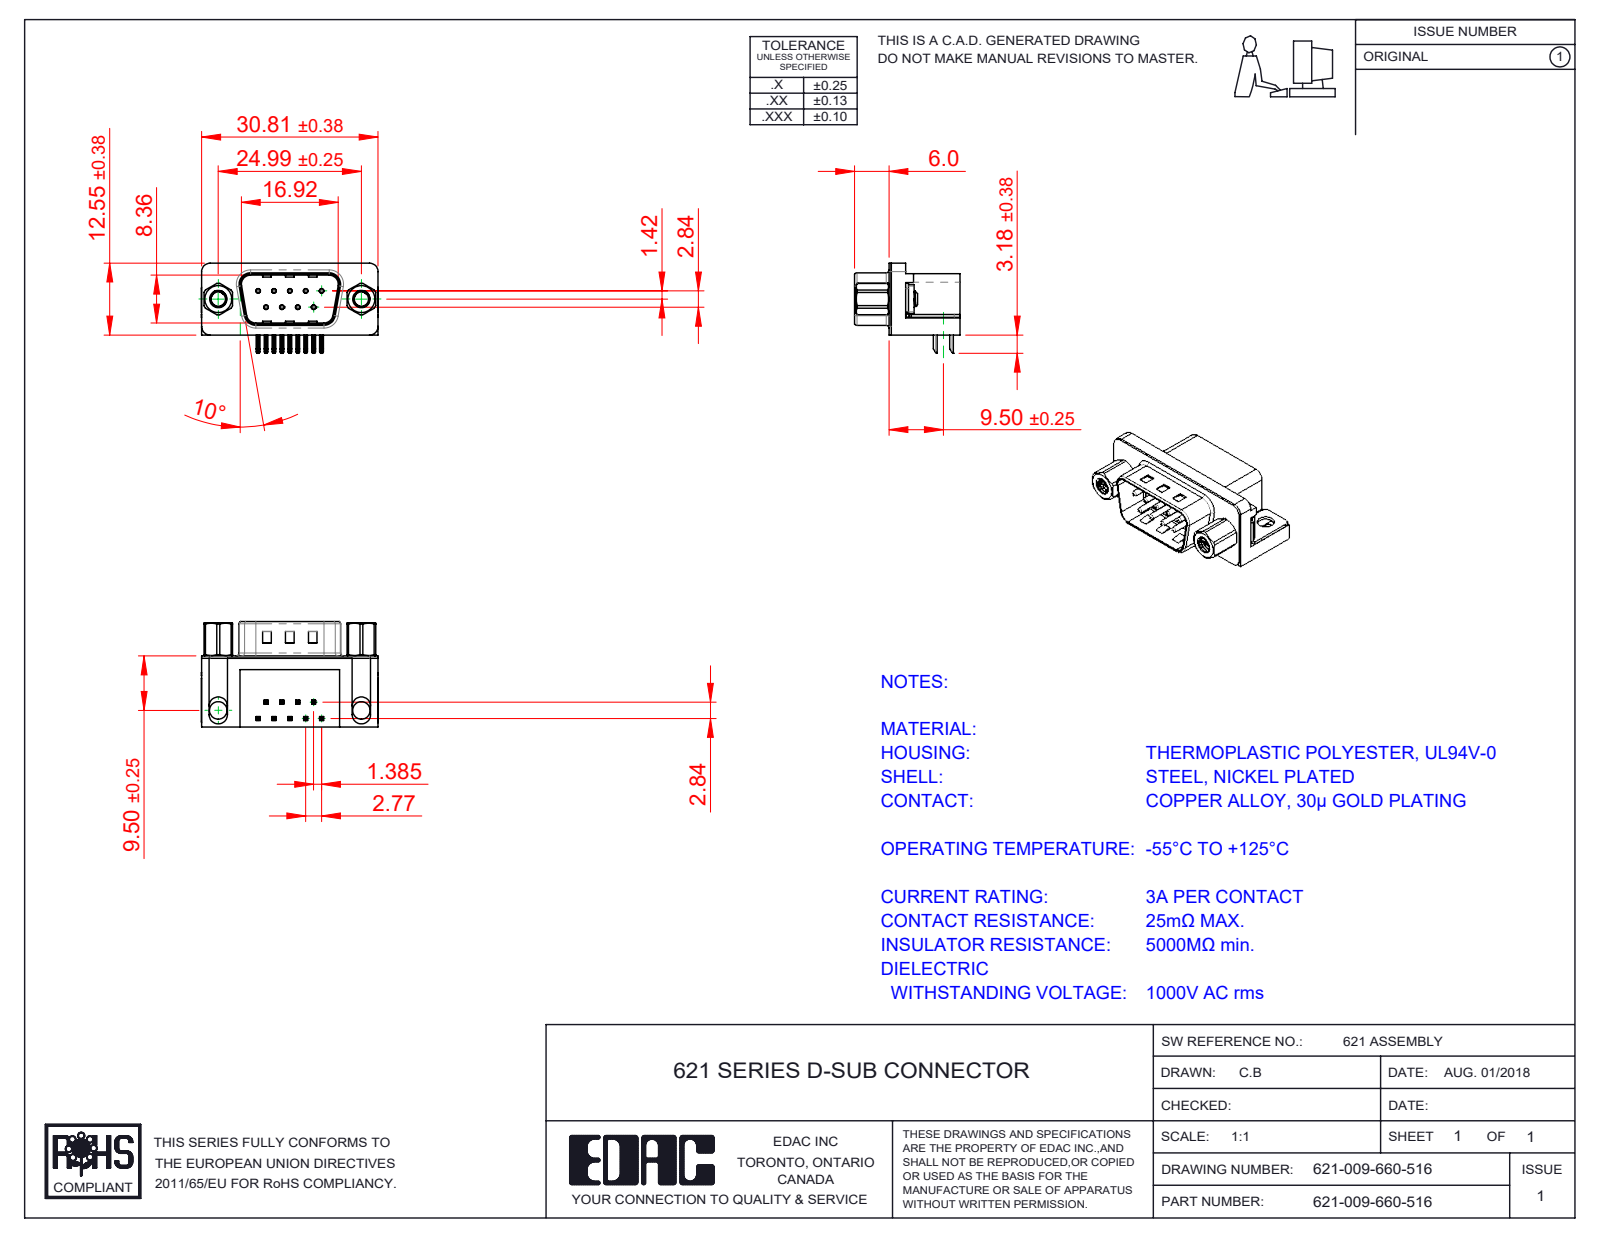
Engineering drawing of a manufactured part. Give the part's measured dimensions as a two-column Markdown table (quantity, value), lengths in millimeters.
| quantity | value |
| --- | --- |
| part name | 621 Housing_9 Socket; 621 Contact Bottom; 621 Shell_9 Socket; 621-009-660-516 (+4 more) |
| STEP written by | SolidWorks 2016 (CONFIG_CONTROL_DESIGN) |
| units | millimeters |
| bodies | 17 solids, 1137 faces (593 planar, 411 cylindrical, 133 other) |
| overall size | 30.89 × 18.4 × 15.73 |
| volume | 3 483 mm³ |
| surface area | 4 940 mm² |
| round holes (diameter × count) | 0.35 × 9, 0.8 × 9, 2.5 × 2, 3.05 × 2, 4 × 2, 4.8 × 2, 5 × 2 |
| round bosses / shafts (diameter × count) | 0.75 × 9, 4.9 × 2, 4.75 × 2, 3.9 × 2, 3 × 2 |
| partial cylindrical surfaces (radius × count) | 0.25 × 44, 0.12 × 18, 1 × 16, 0.5 × 9, 1.5 × 8, 1.6 × 8, 0.9 × 4, 2 × 4 |
| main face-to-face distances | 0.4, 12, 12.4, 10.35, 0.5, 9.5, 2.5, 2.9, 2.1, 0.35 |
| hole center spacings | 3.16, 2.77, 5.54, 5.03, 5.04, 8.31, 7.48, 7.49 |
